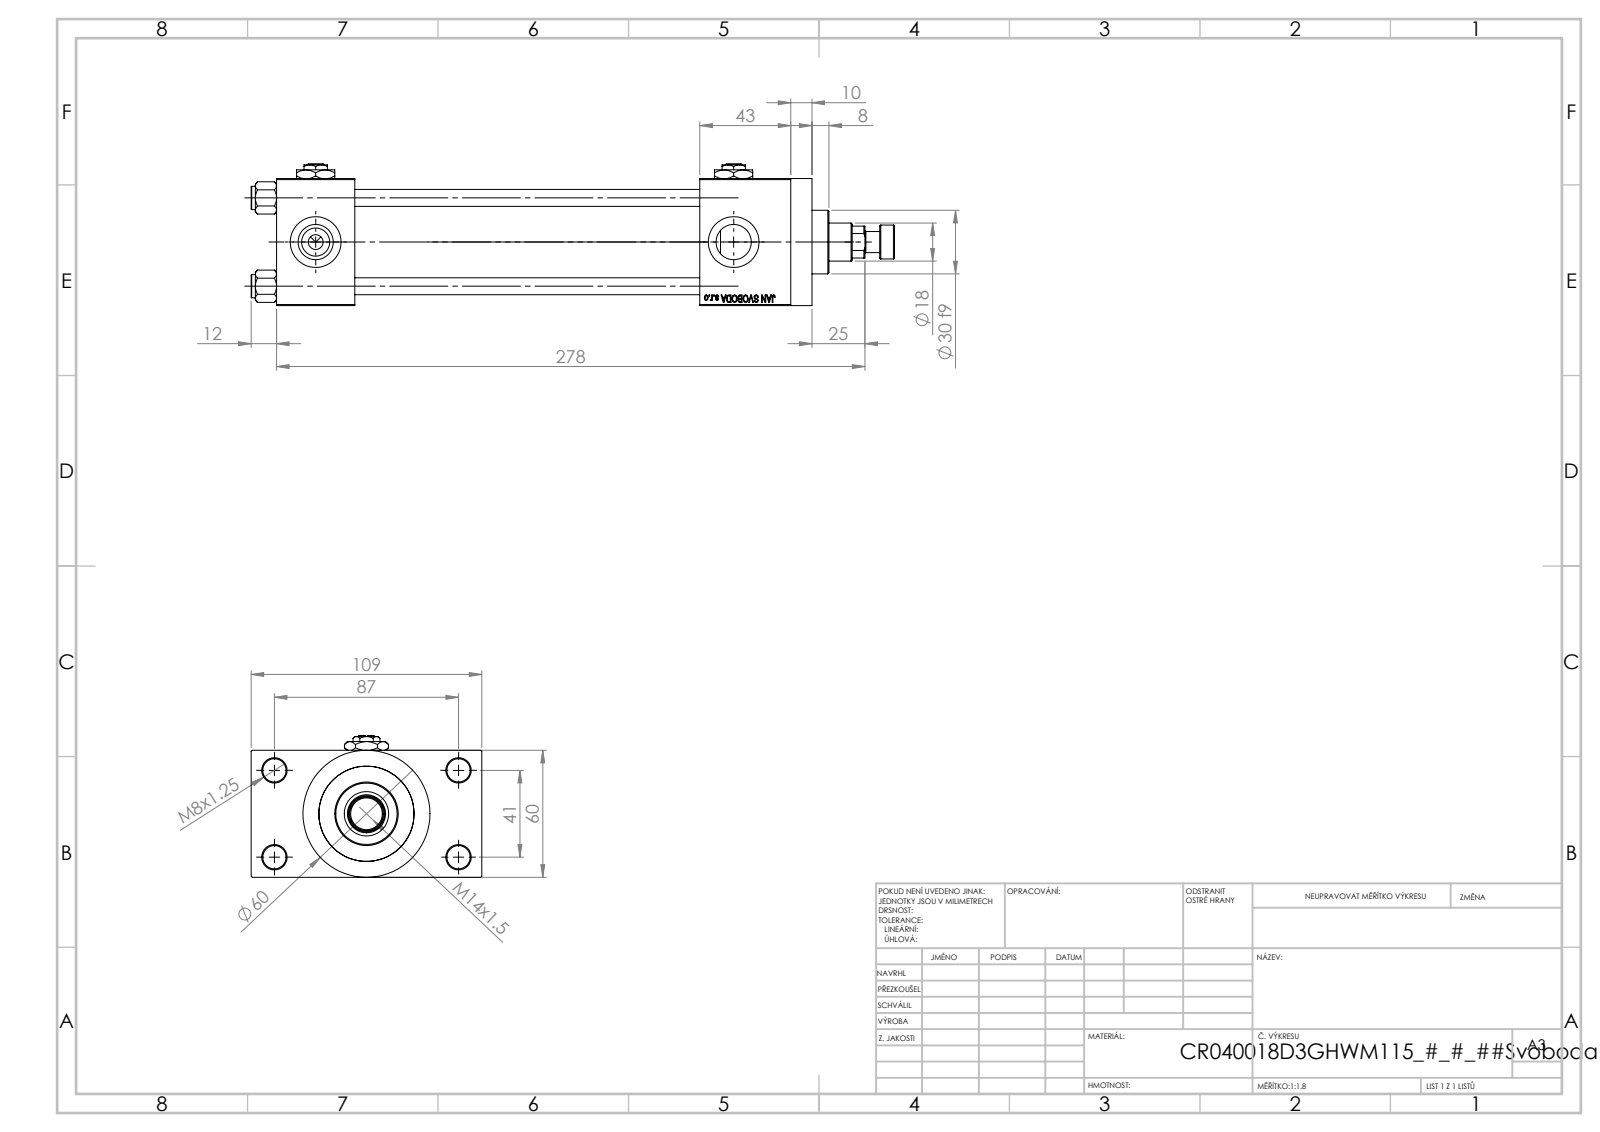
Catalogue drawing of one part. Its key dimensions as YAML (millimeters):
part_name: "V215CR_VCP_D; V215CR_ROD_END_W; V215CR_D_TYCINKA; V215_VC_A (+3 more)"
step_written_by: "SolidWorks 2019 (CONFIG_CONTROL_DESIGN)"
units: millimeters
bodies: {solids: 14, faces: 1218, planar: 549, cylindrical: 103, other: 566}
overall_size: [304, 109, 67]
volume: 602677
surface_area: 171030
round_holes:
  - {diameter: 8, count: 4}
  - {diameter: 11, count: 4}
  - {diameter: 16.66, count: 4}
  - {diameter: 24, count: 4}
  - {diameter: 7, count: 3}
  - {diameter: 8.5, count: 1}
  - {diameter: 18, count: 1}
  - {diameter: 21, count: 1}
  - {diameter: 31, count: 1}
  - {diameter: 40, count: 1}
  - {diameter: 45, count: 1}
round_bosses_or_shafts:
  - {diameter: 11, count: 4}
  - {diameter: 60, count: 1}
  - {diameter: 46, count: 1}
  - {diameter: 30, count: 1}
  - {diameter: 16, count: 1}
  - {diameter: 10, count: 1}
partial_cylinders:
  - {radius: 8.5, count: 1}
face_to_face_distances: [60, 24.5, 163, 84.5, 37, 200, 43, 243, 206, 10]
hole_center_spacings: [22.65, 29.49, 41.7, 47.15, 48.09, 64.35, 76.49, 41]
